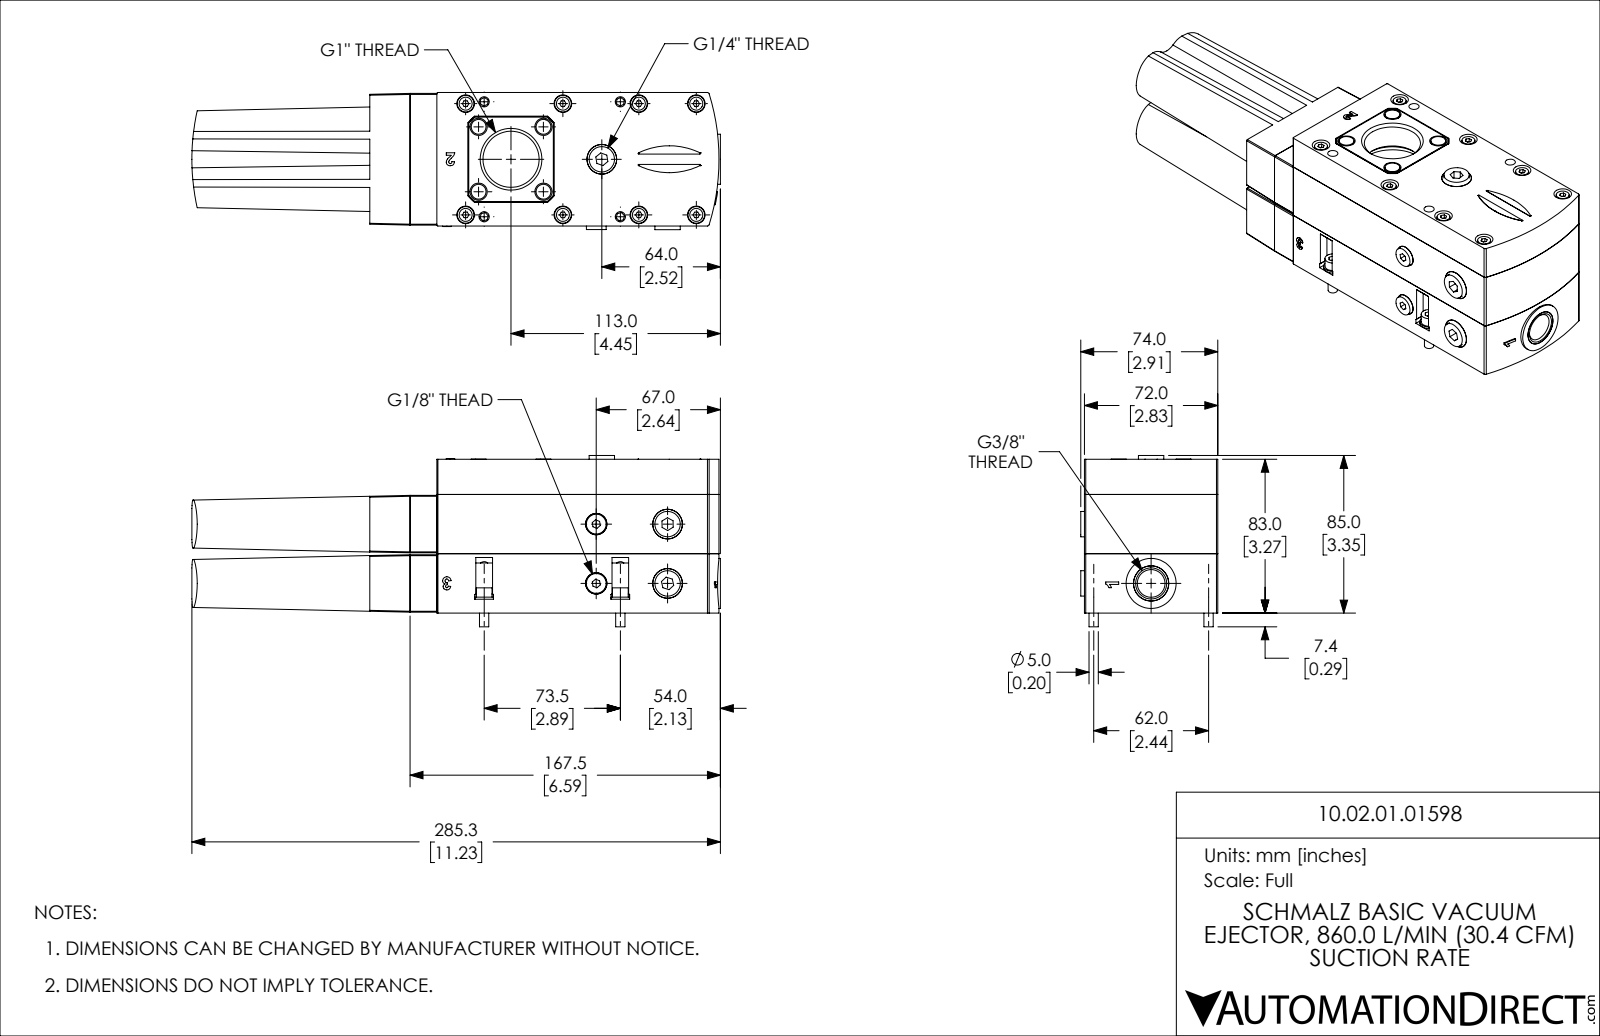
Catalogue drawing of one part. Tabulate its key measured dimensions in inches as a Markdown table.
| quantity | value |
| --- | --- |
| part name | 10.02.01.01598 |
| STEP written by | SolidWorks 2021 (CONFIG_CONTROL_DESIGN) |
| units | inches |
| bodies | 60 solids, 1115 faces (509 planar, 491 cylindrical, 115 other) |
| overall size | 11.23 × 3.638 × 2.913 |
| volume | 76.89 in³ |
| surface area | 345.3 in² |
| round holes (diameter × count) | 0.169 × 12, 0.177 × 12, 0.374 × 10, 0.13 × 8, 0.244 × 8, 0.256 × 8, 0.453 × 6, 0.138 × 4, 0.173 × 4, 0.209 × 4, 0.217 × 4, 0.315 × 4 |
| round bosses / shafts (diameter × count) | 0.276 × 12, 0.157 × 12, 0.354 × 8, 0.236 × 8, 0.394 × 4, 0.335 × 4, 0.315 × 4, 0.197 × 4 |
| partial cylindrical surfaces (radius × count) | 0.02 × 22, 0.181 × 8, 0.177 × 4, 0.199 × 4, 0.013 × 2, 0.013 × 2, 0.039 × 2, 0.373 × 2 |
| main face-to-face distances | 1.26, 2.835, 2.52, 0.571, 0.748, 3.268, 2.008, 0.02, 1.24, 2.5 |
| hole center spacings | 1.371, 1.26, 1.364, 0.396, 0.776, 0.964, 0.974, 1.33 |
